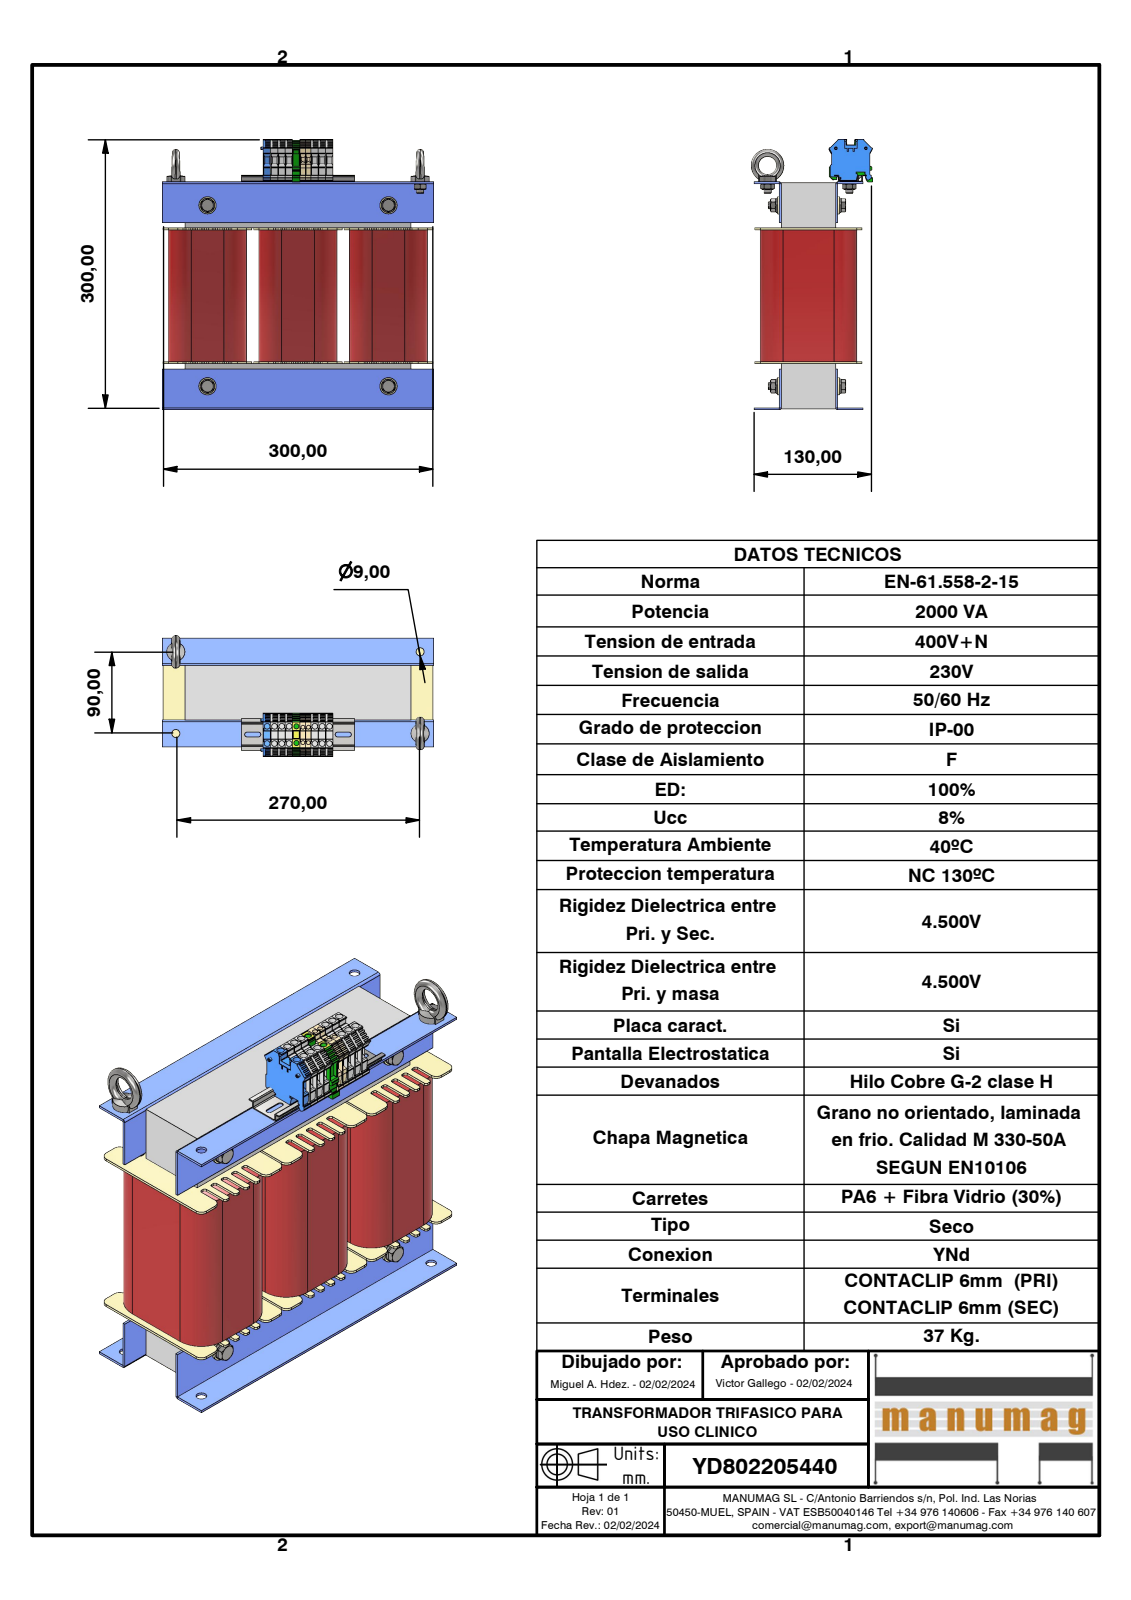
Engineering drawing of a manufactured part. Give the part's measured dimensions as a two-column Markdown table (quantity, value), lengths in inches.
| quantity | value |
| --- | --- |
| part name | YD802205440; 3UI150 250 x 250 - 60 (Rc50); RC50 NT050; DIN 125 - A 8,4 (+8 more) |
| STEP written by | Autodesk Inventor 2023 (AUTOMOTIVE_DESIGN) |
| units | inches |
| bodies | 47 solids, 3625 faces (2514 planar, 893 cylindrical, 218 other) |
| overall size | 11.811 × 11.774 × 5.26 |
| volume | 347 in³ |
| surface area | 1 267 in² |
| round holes (diameter × count) | 0.248 × 14, 0.262 × 6, 0.433 × 6, 0.094 × 4, 0.098 × 4, 0.108 × 4, 0.169 × 4, 0.315 × 4, 0.331 × 4, 0.354 × 4, 0.413 × 4, 0.116 × 2 |
| round bosses / shafts (diameter × count) | 0.748 × 4, 0.63 × 4, 0.449 × 4, 0.378 × 4, 0.288 × 4, 1.417 × 2, 0.315 × 2, 0.276 × 2 |
| partial cylindrical surfaces (radius × count) | 0.079 × 114, 0.012 × 30, 0.236 × 24, 0.039 × 22, 0.01 × 17, 0.984 × 12, 0.102 × 10, 0.02 × 9 |
| main face-to-face distances | 1.969, 0.079, 3.937, 2.362, 7.874, 5.906, 9.843, 0.039, 2.008, 7.835 |
| hole center spacings | 0.319, 0.813, 0.748, 0.638, 0.983, 1.756, 1.909, 2.075 |
